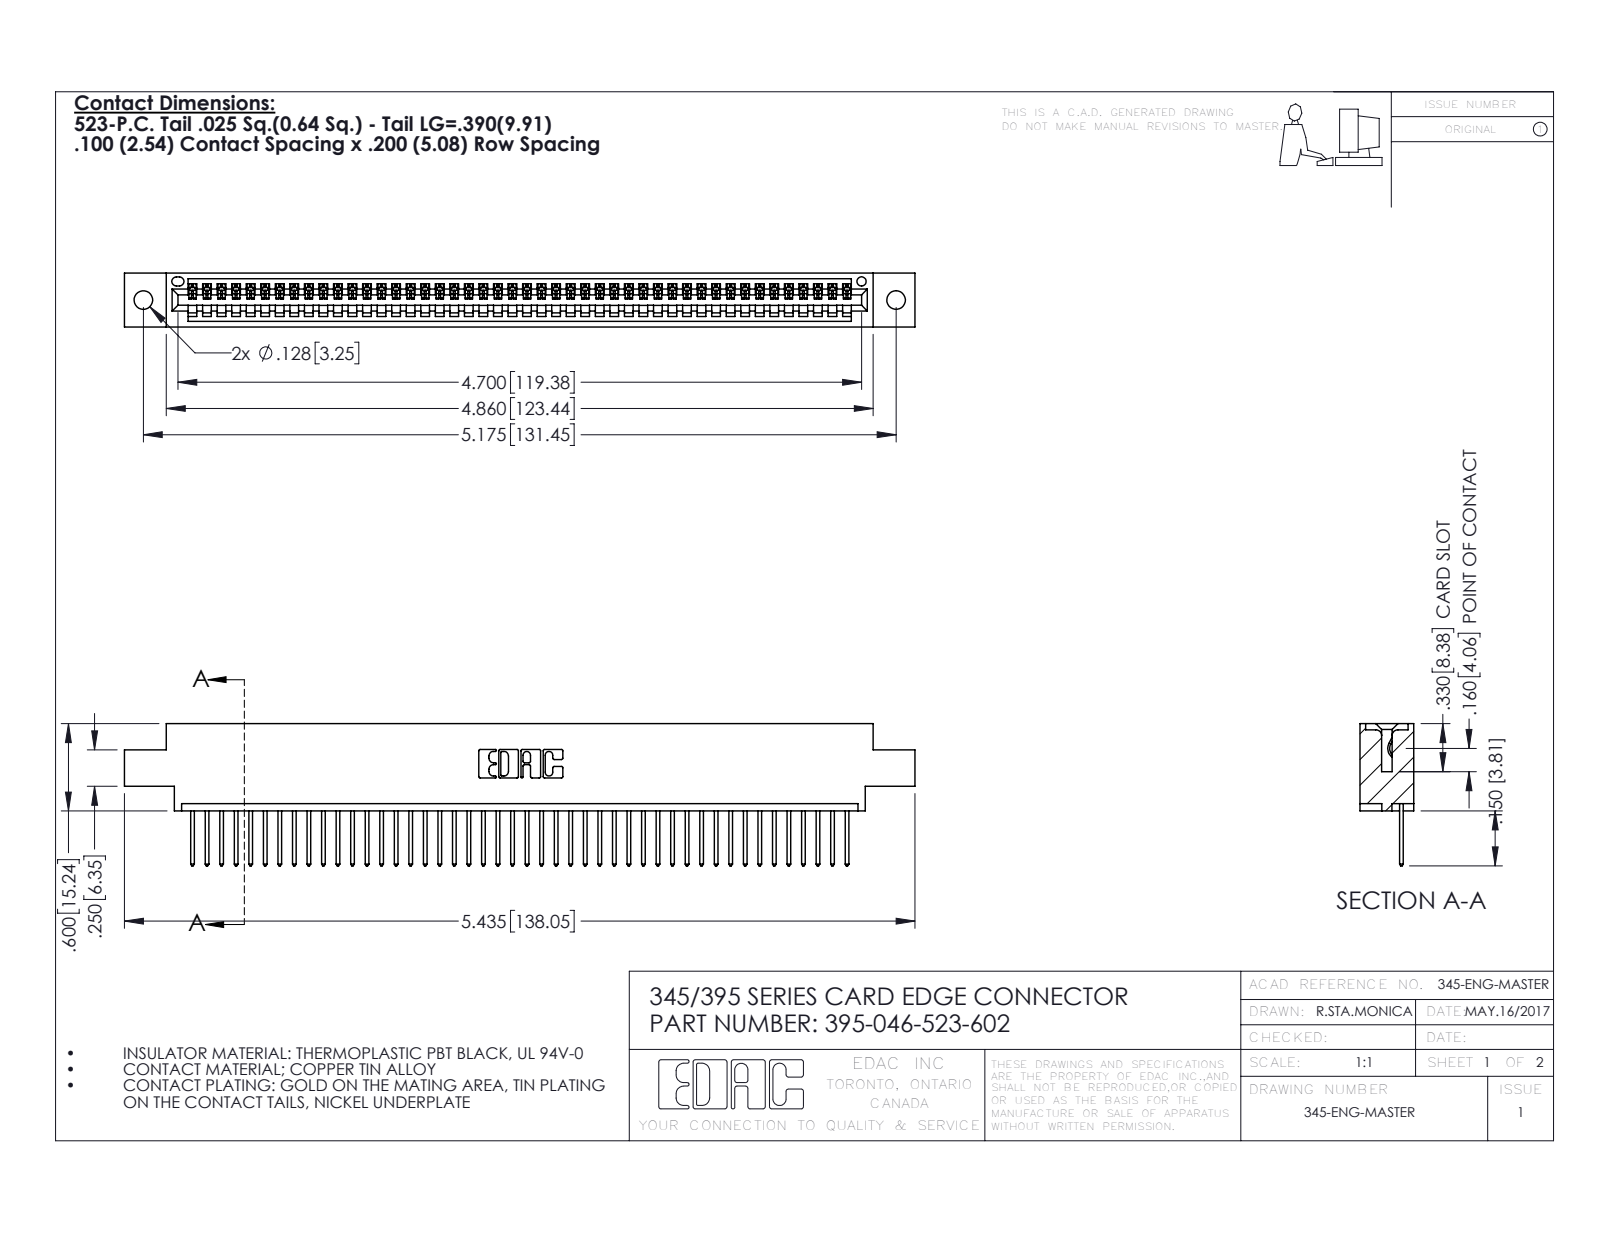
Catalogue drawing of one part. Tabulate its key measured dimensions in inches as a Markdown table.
| quantity | value |
| --- | --- |
| part name | 345 Part_0.170 Offset - 0.128 Dia; 345-292-001_345-293-123; 395-046-523-602 |
| STEP written by | SolidWorks 2016 (CONFIG_CONTROL_DESIGN) |
| units | inches |
| bodies | 47 solids, 2798 faces (1924 planar, 874 cylindrical, 0 other) |
| overall size | 5.435 × 0.977 × 0.37 |
| volume | 0.792 in³ |
| surface area | 26.67 in² |
| round holes (diameter × count) | 0.128 × 2, 0.064 × 1 |
| partial cylindrical surfaces (radius × count) | 0.006 × 92, 0.01 × 92, 0.01 × 22, 0.007 × 6, 0.031 × 6, 0.026 × 3, 0.031 × 2, 0.04 × 2 |
| main face-to-face distances | 0.298, 0.072, 0.37, 0.2, 0.098, 0.272, 0.025, 0.225, 0.175, 0.149 |
| hole center spacings | 0.27, 4.939, 5.175 |
